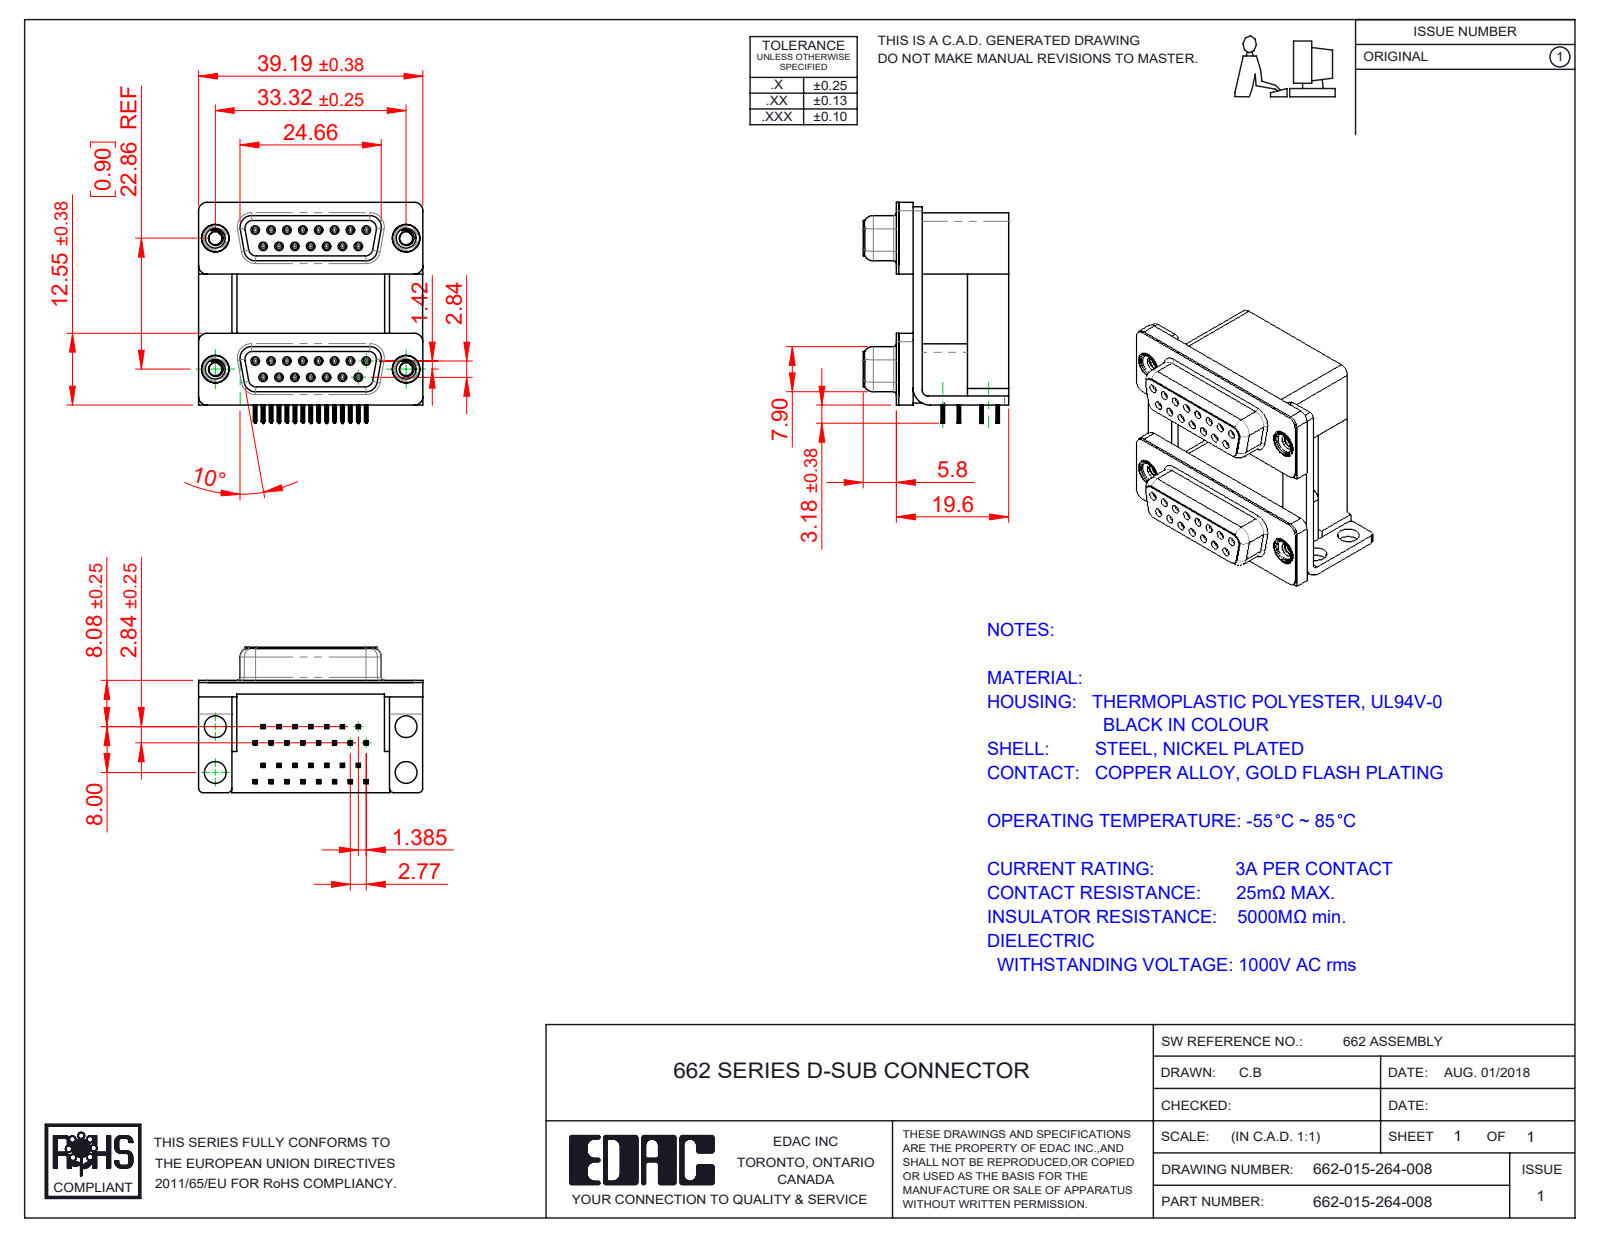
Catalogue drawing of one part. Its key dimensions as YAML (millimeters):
part_name: "662 Threaded Rivet_4-40; 662 Contact Top Lower; 662 Housing Upper_15 Contacts H; 662 Contact Bottom Upper_H (+7 more)"
step_written_by: "SolidWorks 2020 (CONFIG_CONTROL_DESIGN)"
units: millimeters
bodies: {solids: 41, faces: 4862, planar: 2196, cylindrical: 1174, other: 1492}
overall_size: [39.19, 38.59, 25.4]
volume: 16762
surface_area: 18594
round_holes:
  - {diameter: 0.8, count: 30}
  - {diameter: 0.9, count: 30}
  - {diameter: 2.26, count: 4}
  - {diameter: 3.5, count: 4}
  - {diameter: 3.8, count: 4}
  - {diameter: 4, count: 4}
  - {diameter: 4.8, count: 4}
  - {diameter: 5, count: 4}
round_bosses_or_shafts:
  - {diameter: 1.2, count: 30}
  - {diameter: 4.9, count: 4}
  - {diameter: 4.75, count: 4}
  - {diameter: 3.9, count: 4}
partial_cylinders:
  - {radius: 0.1, count: 240}
  - {radius: 0.15, count: 120}
  - {radius: 0.35, count: 60}
  - {radius: 0.34, count: 30}
  - {radius: 1.35, count: 16}
  - {radius: 1.5, count: 16}
  - {radius: 0.28, count: 14}
  - {radius: 0.5, count: 8}
face_to_face_distances: [19.2, 22.86, 0.4, 7.2, 12, 9.5, 16.7, 2.5, 10.7, 2.9]
hole_center_spacings: [3.16, 23.03, 2.77, 23.52, 5.54, 8.31, 22.86, 24.32]
